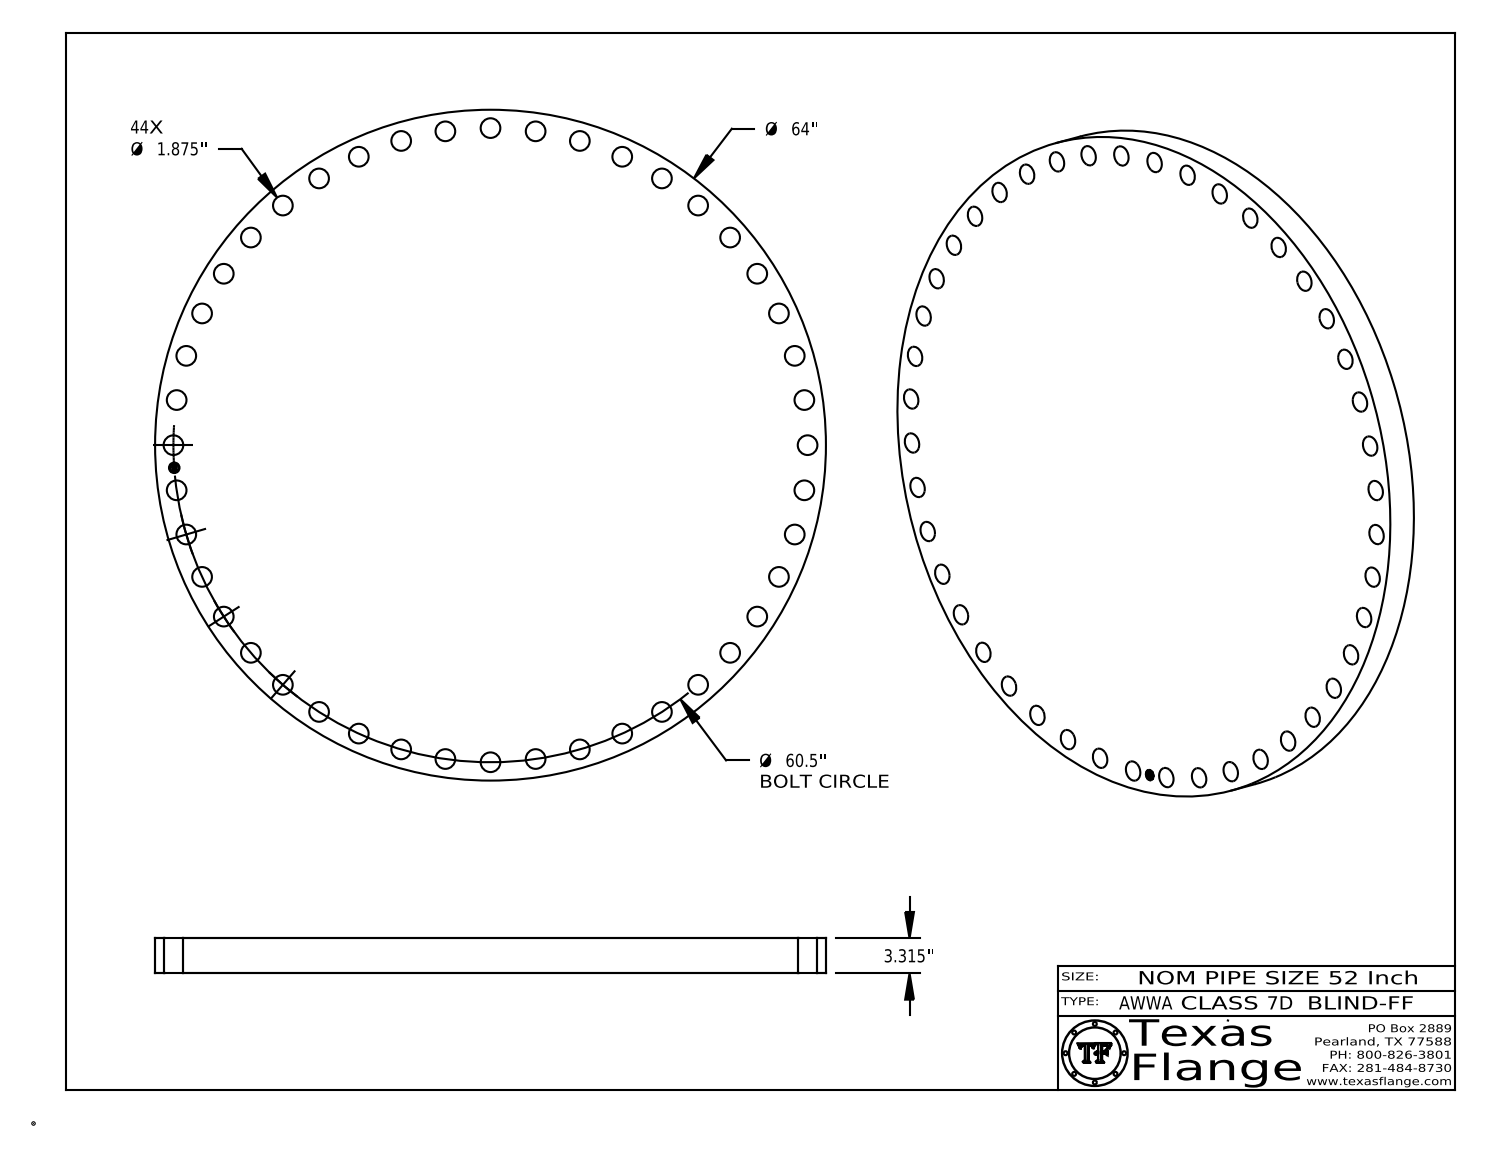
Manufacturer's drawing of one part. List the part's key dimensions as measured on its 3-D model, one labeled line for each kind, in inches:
Part name (STEP PRODUCT): AWWA Class 7D-BLIND-FF
STEP written by: CATIA V5 STEP AP214 (AUTOMOTIVE_DESIGN)
Units: inches
Bodies: 1 solid, 477 faces (367 planar, 110 cylindrical, 0 other)
Overall size (bounding box): 64 × 64 × 3.315
Volume: 10 262 in³ · Surface area: 7 717 in²
Round holes (diameter × count): ⌀1.875 ×44, ⌀1 ×1
Round bosses / shafts (diameter × count): ⌀0.061 ×8, ⌀64 ×1, ⌀0.788 ×1
Main face-to-face distances: 3.315, 0.015, 3.3, 0.298, 0.292, 0.019, 0.054, 0.193, 0.248, 0.044
Hole centre spacings: 4.316, 8.61, 21.143, 25.133, 17.045, 42.78, 48.433, 59.884
